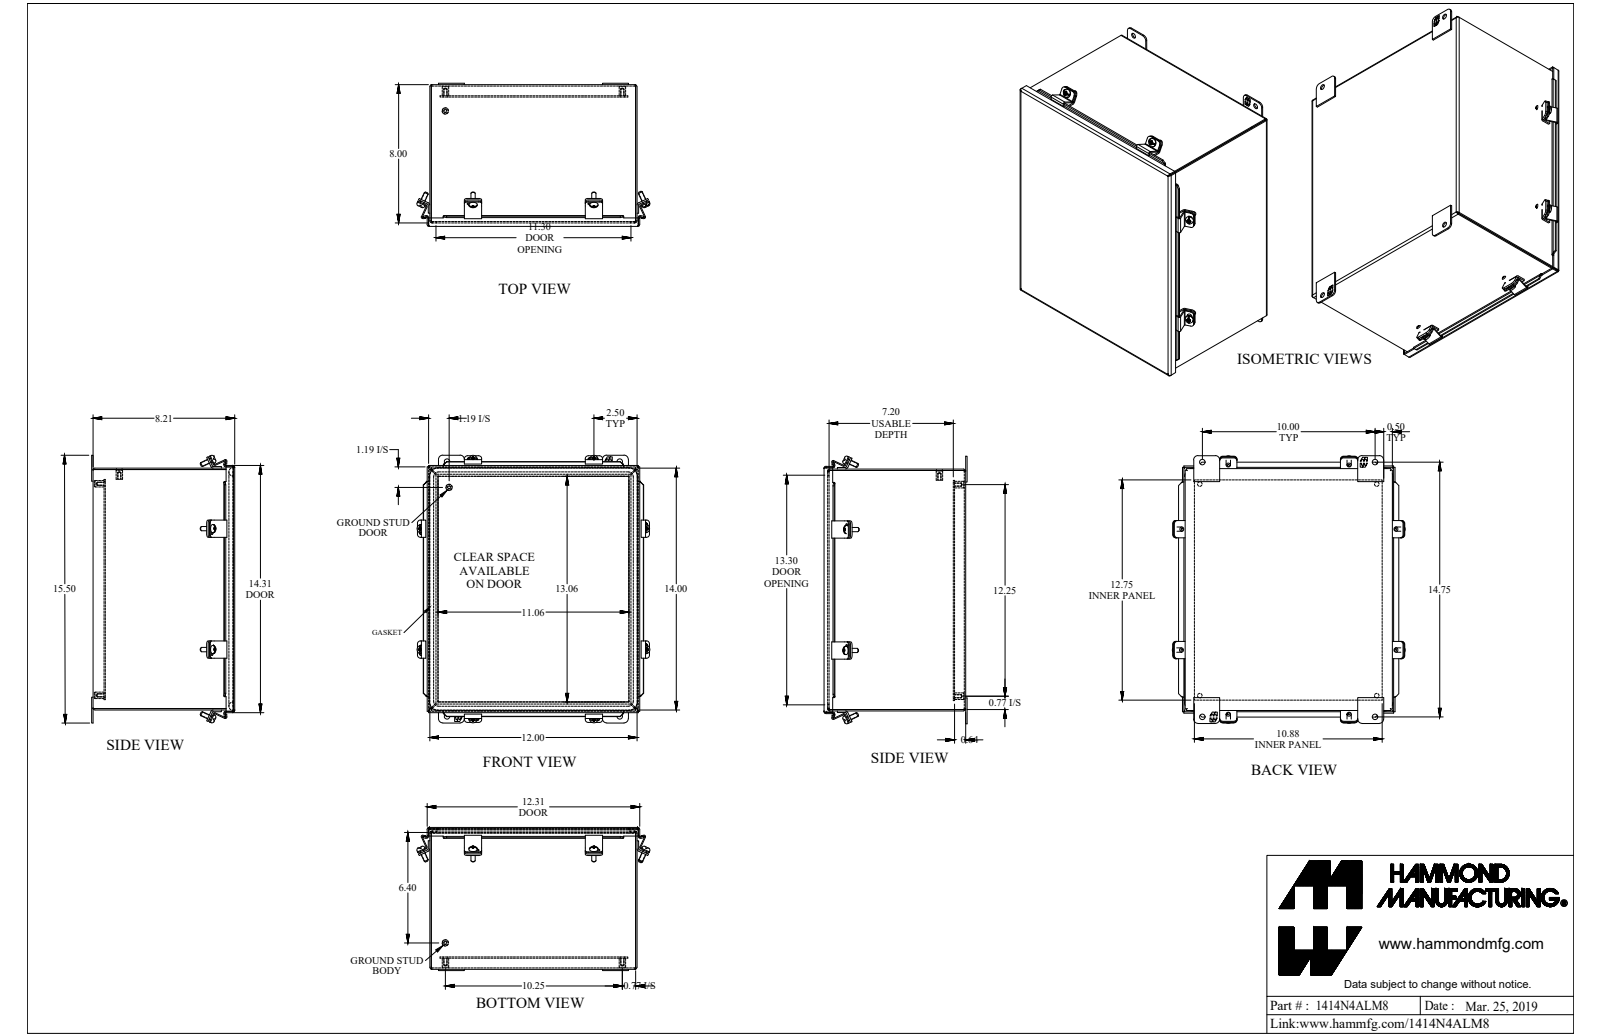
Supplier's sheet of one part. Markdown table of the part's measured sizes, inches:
| quantity | value |
| --- | --- |
| part name | 1414N4ALM8 |
| STEP written by | SolidWorks 2018 (AUTOMOTIVE_DESIGN) |
| units | inches |
| bodies | 38 solids, 1051 faces (719 planar, 238 cylindrical, 94 other) |
| overall size | 15.5 × 13.49 × 8.286 |
| volume | 82.17 in³ |
| surface area | 2 081 in² |
| round holes (diameter × count) | 0.213 × 8, 0.159 × 6, 0.265 × 4, 0.313 × 4 |
| round bosses / shafts (diameter × count) | 0.48 × 8, 0.25 × 8, 0.375 × 6, 0.33 × 6 |
| partial cylindrical surfaces (radius × count) | 0.188 × 24, 0.141 × 16, 0.25 × 12, 0.01 × 10, 0.029 × 8, 0.036 × 8, 0.048 × 8, 0.086 × 8 |
| main face-to-face distances | 0.081, 8.125, 11.919, 13.919, 8.206, 8.044, 0.562, 0.643, 7.563, 7.482 |
| hole center spacings | 7, 10, 10.25, 12.25, 14.75, 15.972, 17.82, 0.31 |
